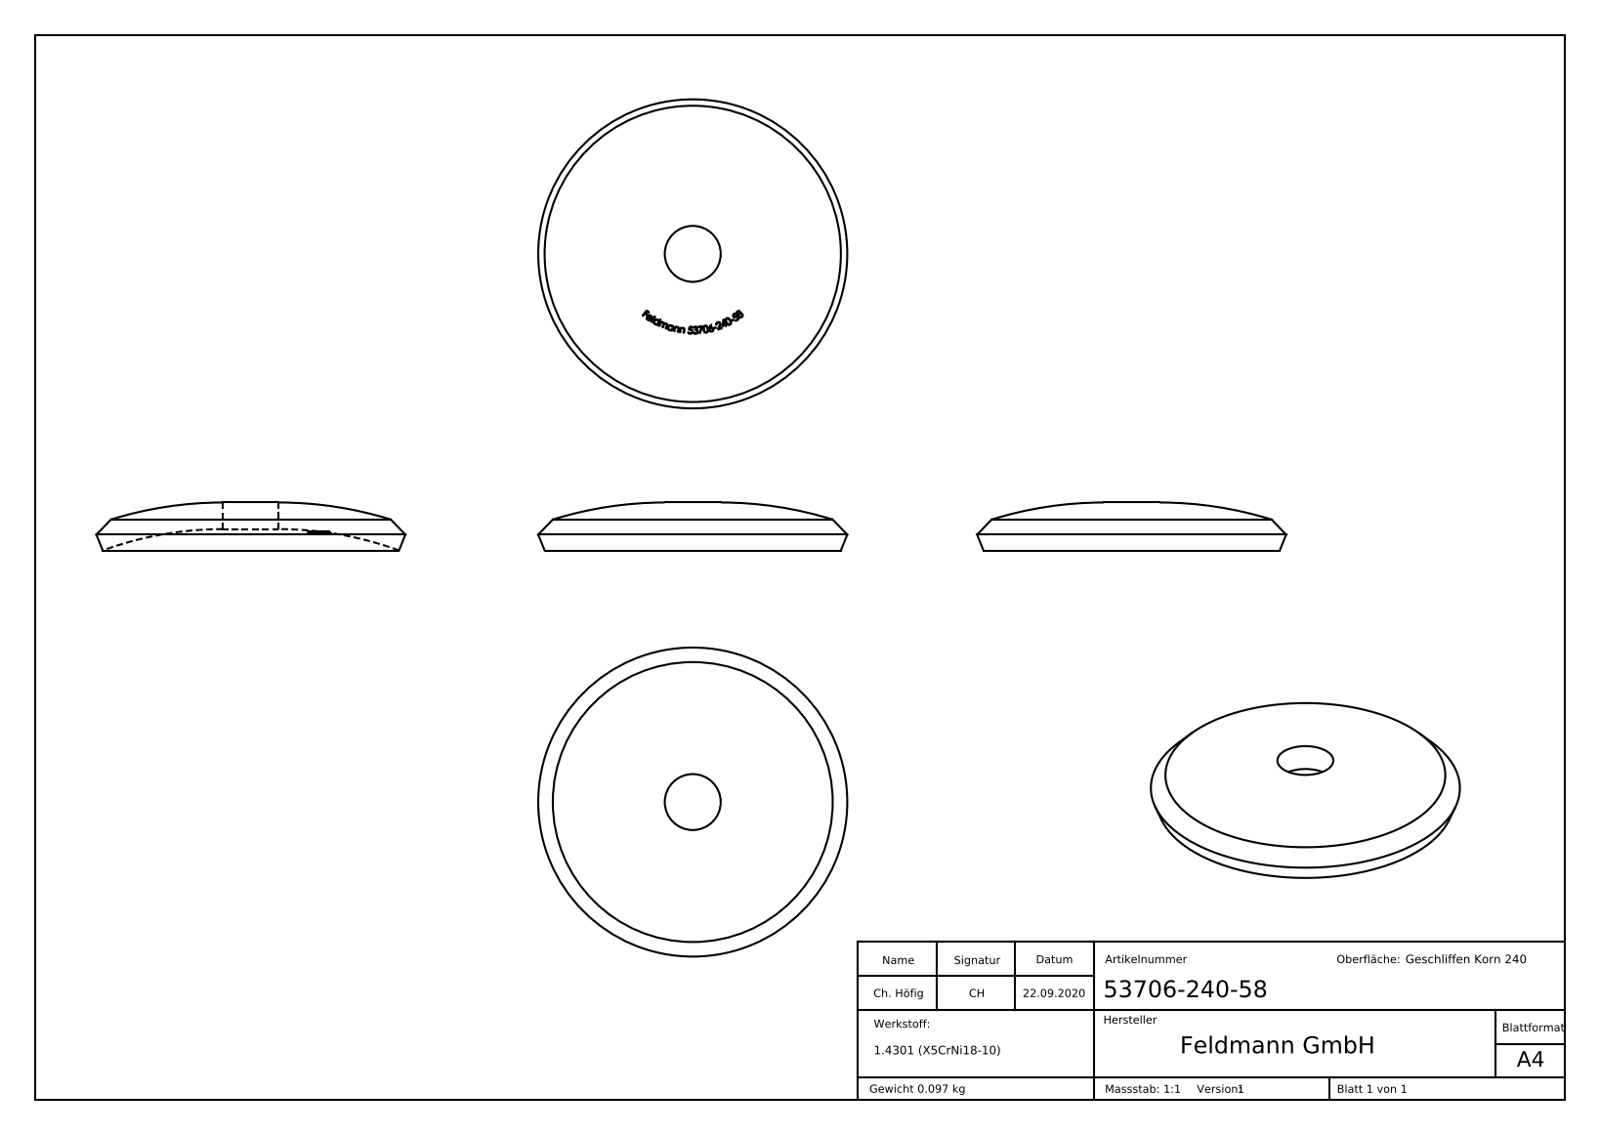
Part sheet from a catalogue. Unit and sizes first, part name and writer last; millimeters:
Units: millimetres
Overall size (bounding box): 58 × 58 × 9
Round holes (diameter × count): ⌀10.5 ×1
Main face-to-face distances: 0.54, 1.33, 0.73, 1.46, 0.67, 0.41, 0.85, 1.2, 0.97, 1.96
Volume: 12 314 mm³ · Surface area: 5 962 mm²
Bodies: 1 solid, 272 faces (105 planar, 2 cylindrical, 165 other)
Part name (STEP PRODUCT): 53706-240-58
STEP written by: SolidWorks 2018 (CONFIG_CONTROL_DESIGN)
